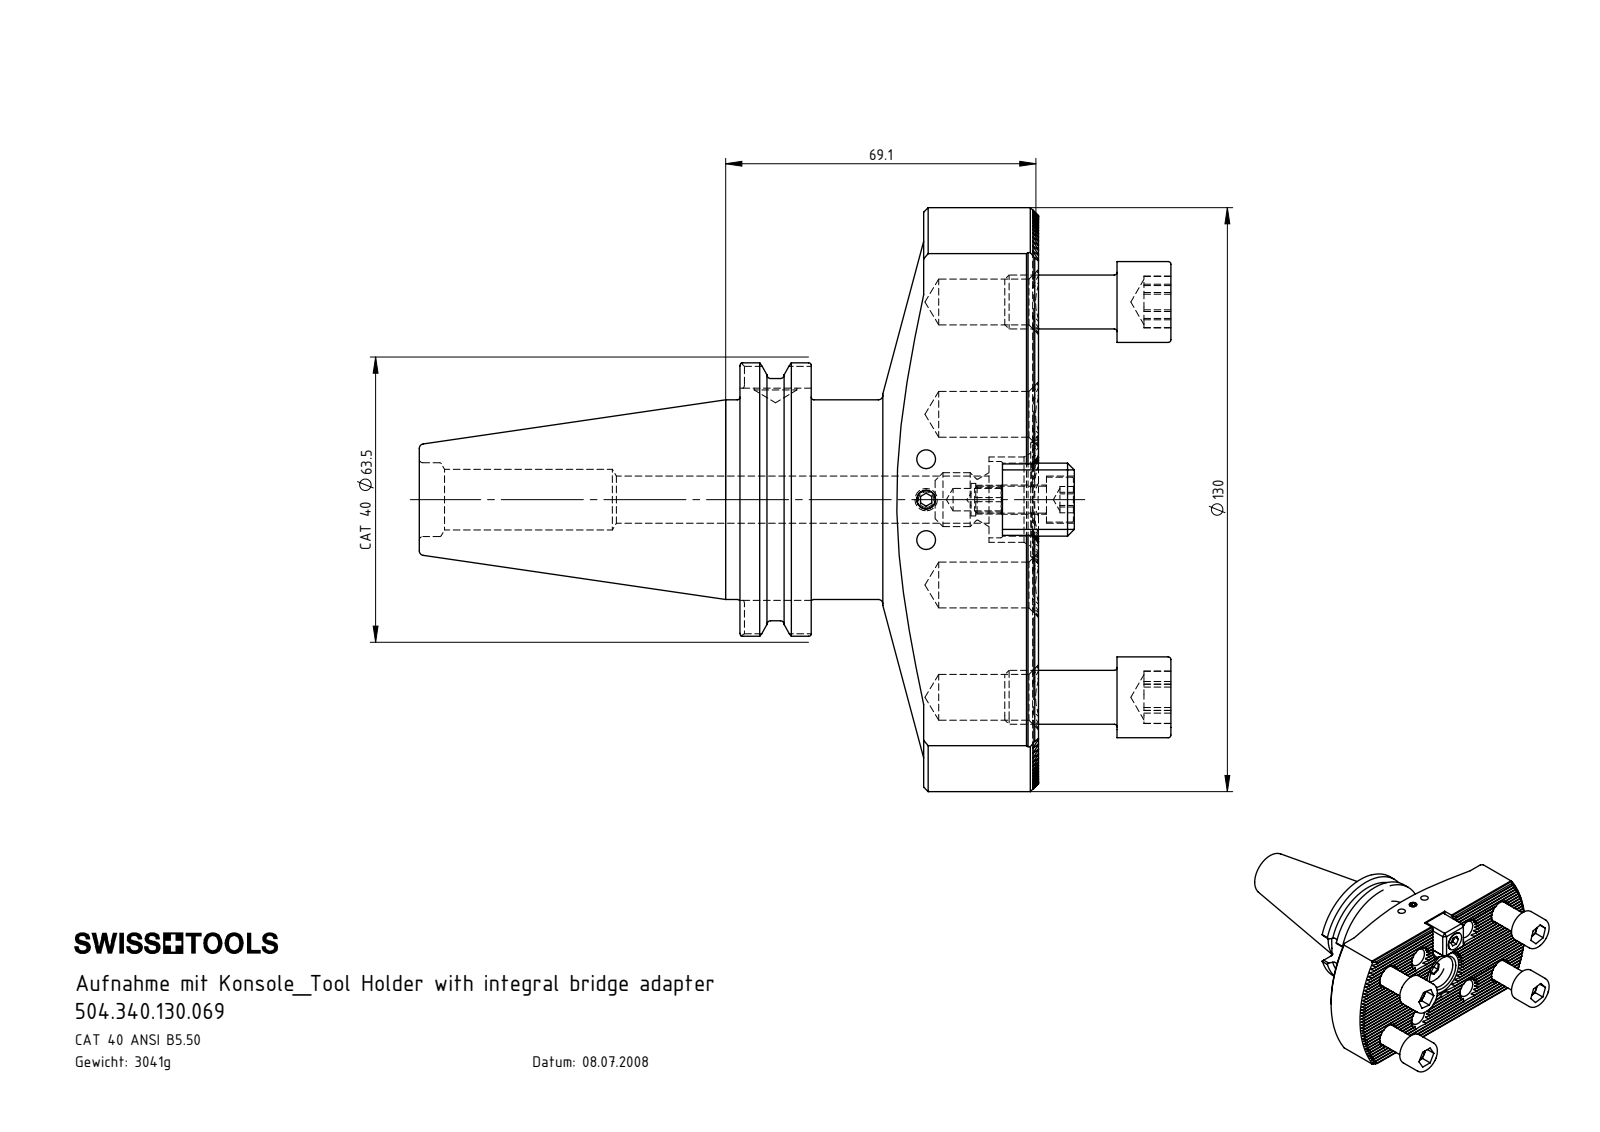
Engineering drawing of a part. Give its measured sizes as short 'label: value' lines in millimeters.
name: ISO 4026 - M5 x 8; DIN 908 - M12x1.5; CT4-Ko1.K01.069_A; 504.340.130.069 (+3 more)
written by: SolidWorks 2017 (CONFIG_CONTROL_DESIGN)
unit: mm
bodies: 10 solids, 856 faces (496 planar, 201 cylindrical, 159 other)
size: 167.42 × 130 × 70
volume: 387 391 mm³; area: 72 839 mm²
holes: 8× ⌀10.2, 3× ⌀4.2, 2× ⌀10.5, 1× ⌀5, 1× ⌀6.5, 1× ⌀7.24, 1× ⌀9.5, 1× ⌀13.5, 1× ⌀16.43, 1× ⌀19
bosses: 5× ⌀12, 4× ⌀18, 1× ⌀63.5, 1× ⌀56.36, 1× ⌀44.45, 1× ⌀17, 1× ⌀10, 1× ⌀6
rounds: 34× R0.14, 8× R0.8, 1× R7.95, 1× R65
face distances: 1.73, 17.32, 70, 8.66, 3.46, 5.2, 6.93, 15.59, 19.05, 3.47
hole spacings: 25, 27.59, 40, 47.17, 48.33, 63, 74.63, 9
